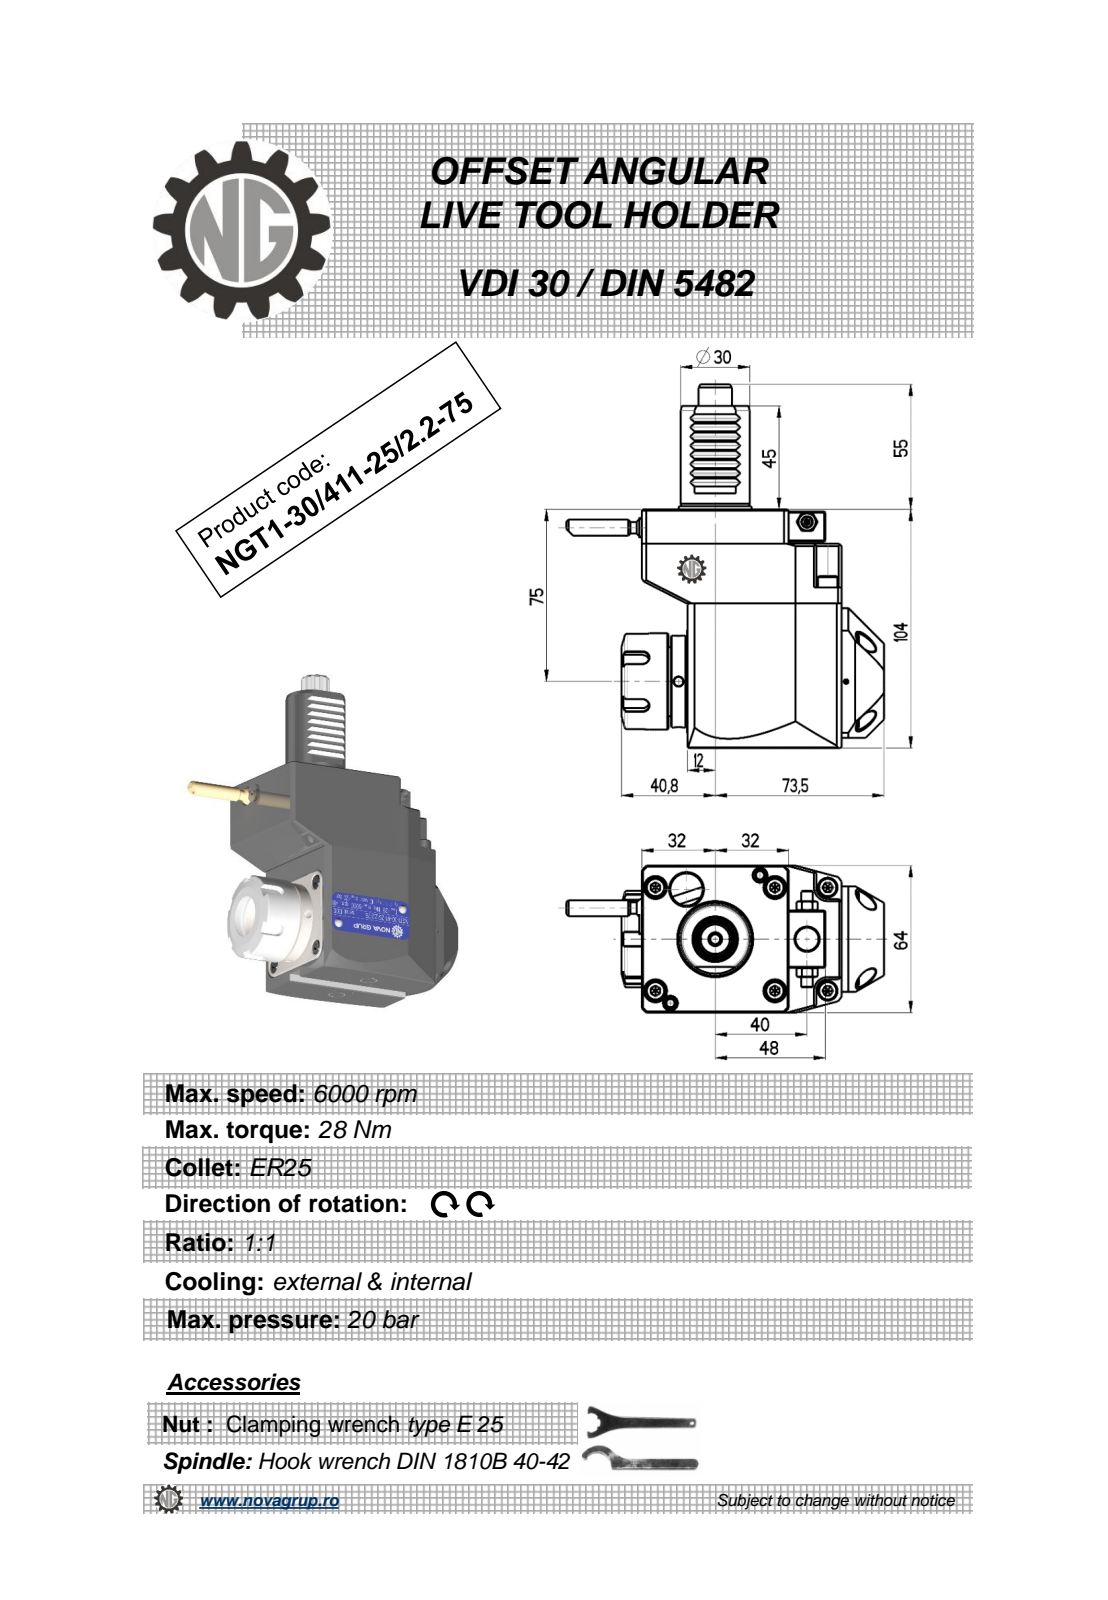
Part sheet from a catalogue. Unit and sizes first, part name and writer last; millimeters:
Units: millimetres
Overall size (bounding box): 159 × 138.38 × 65.4
Round holes (diameter × count): ⌀4 ×2, ⌀4.2 ×2, ⌀2.5 ×1, ⌀3 ×1, ⌀9.5 ×1, ⌀10 ×1, ⌀20.3 ×1
Round bosses / shafts (diameter × count): ⌀8.96 ×2, ⌀5 ×2, ⌀42 ×1, ⌀40 ×1, ⌀33 ×1, ⌀30 ×1, ⌀7 ×1
Partial cylindrical surfaces — rounded edges, fillets, slot ends (radius × count): R2.81 ×16, R0.26 ×12, R0.3 ×8, R3 ×5, R4 ×2, R5.67 ×1, R7.25 ×1, R32 ×1
Main face-to-face distances: 64, 104, 87, 67.2, 19.8, 20, 15, 89, 67, 85.5
Hole centre spacings: 13.54, 15.95, 40, 55.95, 68, 68.35, 89.22
Volume: 560 514 mm³ · Surface area: 53 476 mm²
Bodies: 1 solid, 469 faces (200 planar, 116 cylindrical, 153 other)
Part name (STEP PRODUCT): NGT1_30_411_25_2_2_75
STEP written by: PRO/ENGINEER BY PARAMETRIC TECHNOLOGY CORPORATION, 2010280 (CONFIG_CONTROL_DESIGN)
